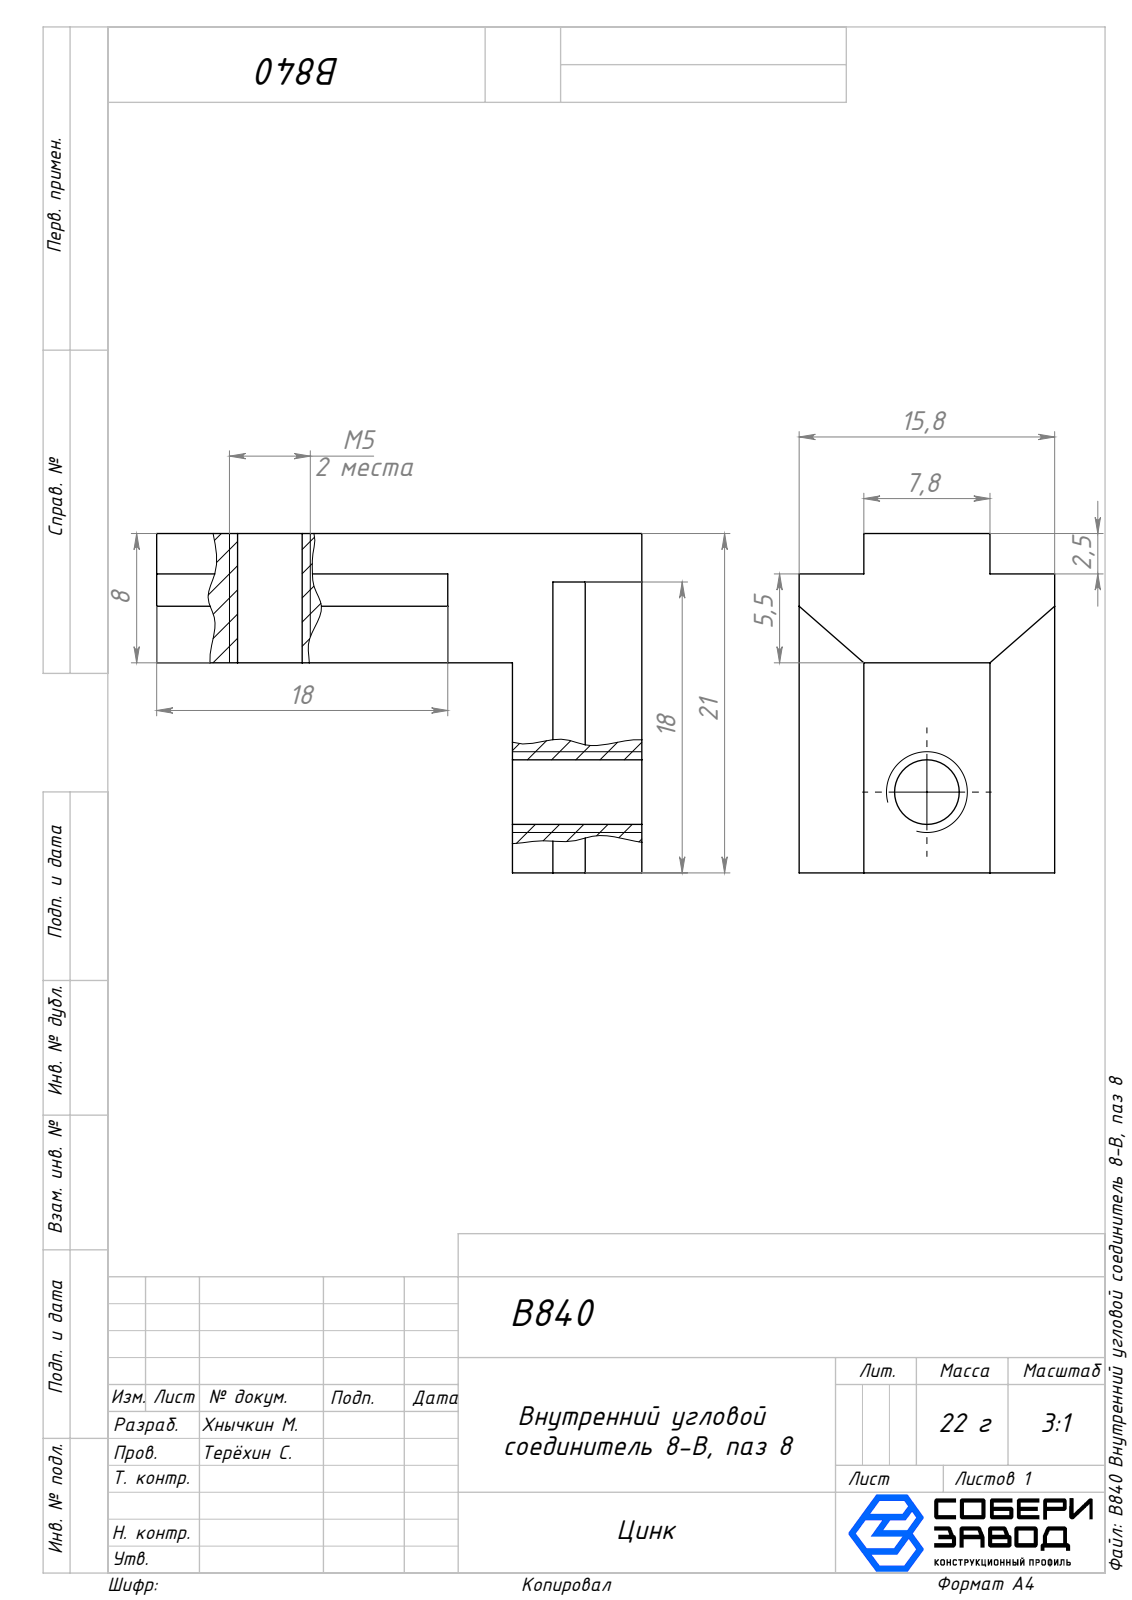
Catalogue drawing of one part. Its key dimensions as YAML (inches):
part_name: "B840 Внутренний угловой соединитель 8-В, паз 8"
step_written_by: "SolidWorks 2025 (AUTOMOTIVE_DESIGN)"
units: inches
bodies: {solids: 1, faces: 28, planar: 24, cylindrical: 4, other: 0}
overall_size: [1.181, 0.827, 0.622]
volume: 0.217
surface_area: 3.368
round_holes:
  - {diameter: 0.157, count: 2}
face_to_face_distances: [0.217, 0.315, 0.098, 0.157, 0.307, 0.465, 0.512, 0.728, 0.827, 0.965]
